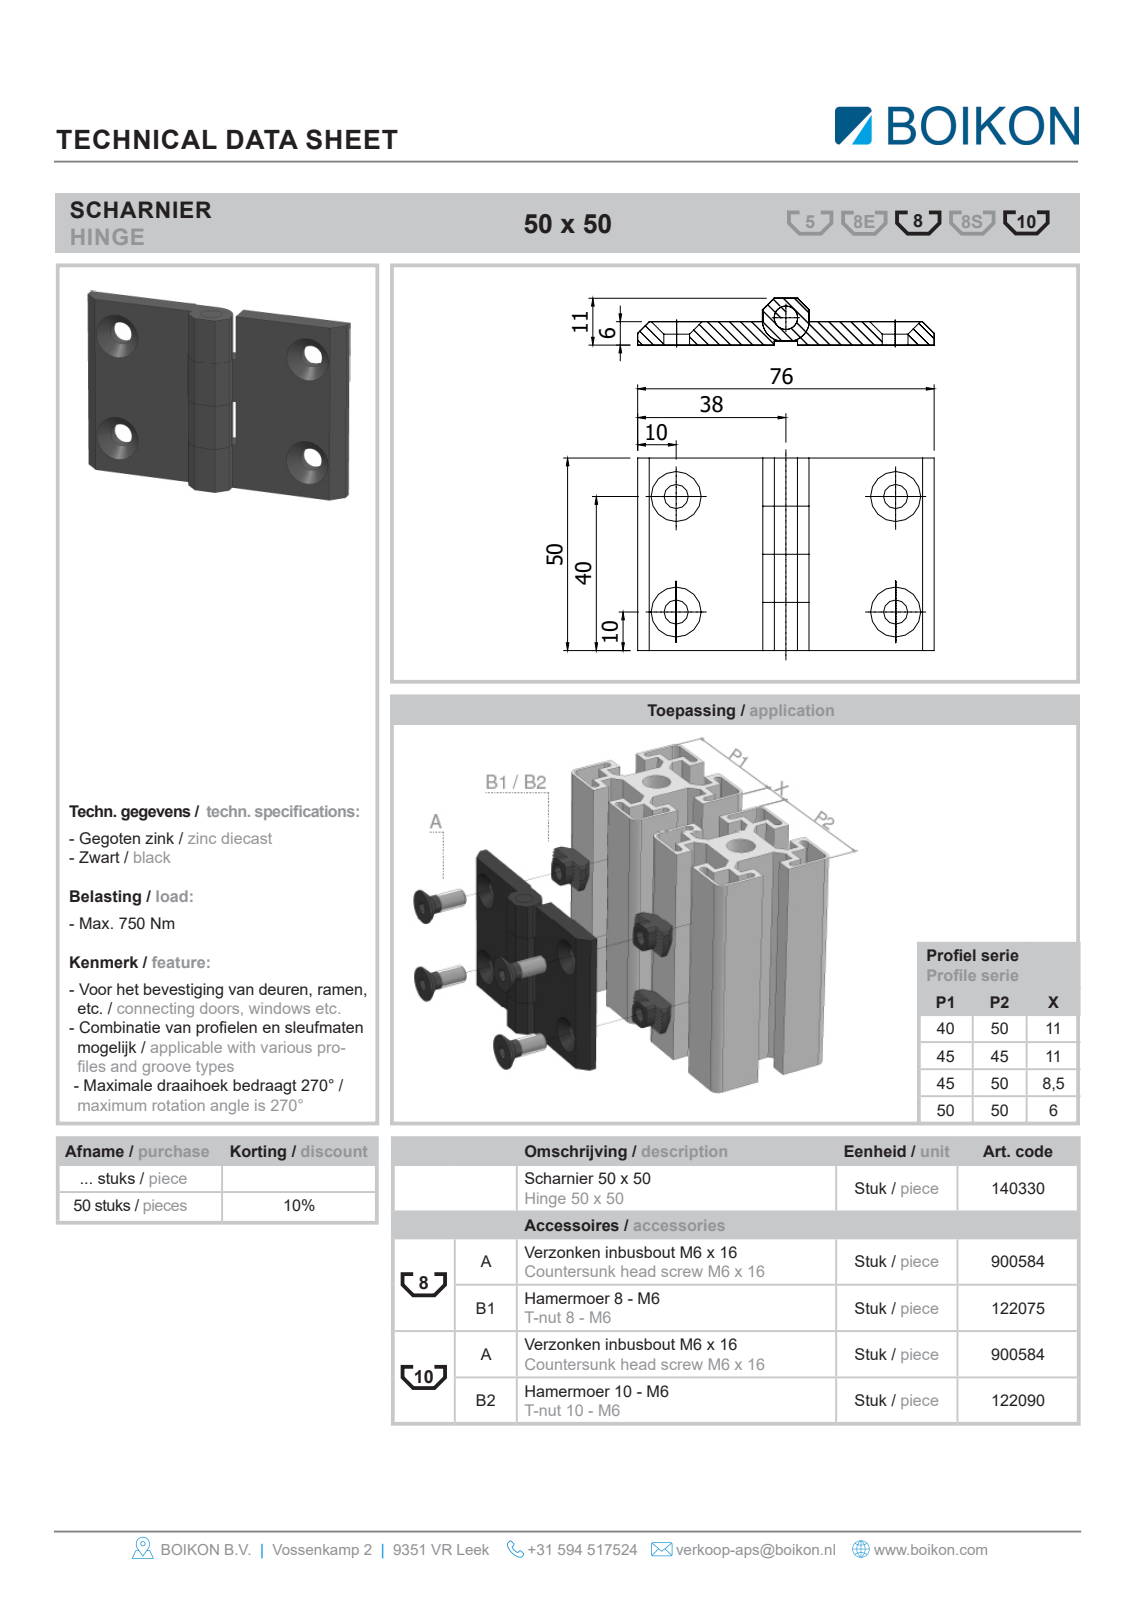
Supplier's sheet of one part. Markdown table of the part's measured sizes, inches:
| quantity | value |
| --- | --- |
| part name | Root; 140330 Scharnier 50x50BOIKON |
| STEP written by | HiCAD 2013 1802.4 Build 509 (AUTOMOTIVE_DESIGN) |
| units | inches |
| bodies | 3 solids, 63 faces (46 planar, 13 cylindrical, 4 other) |
| overall size | 2.992 × 1.969 × 0.453 |
| volume | 1.392 in³ |
| surface area | 19.03 in² |
| round holes (diameter × count) | 0.248 × 4, 0.236 × 1 |
| partial cylindrical surfaces (radius × count) | 0.236 × 1 |
| main face-to-face distances | 0.236, 0.492, 0.217, 0.984, 1.969, 0.724, 1.476, 0.02, 0.453, 0.433 |
| hole center spacings | 1.181, 2.205, 2.501 |
